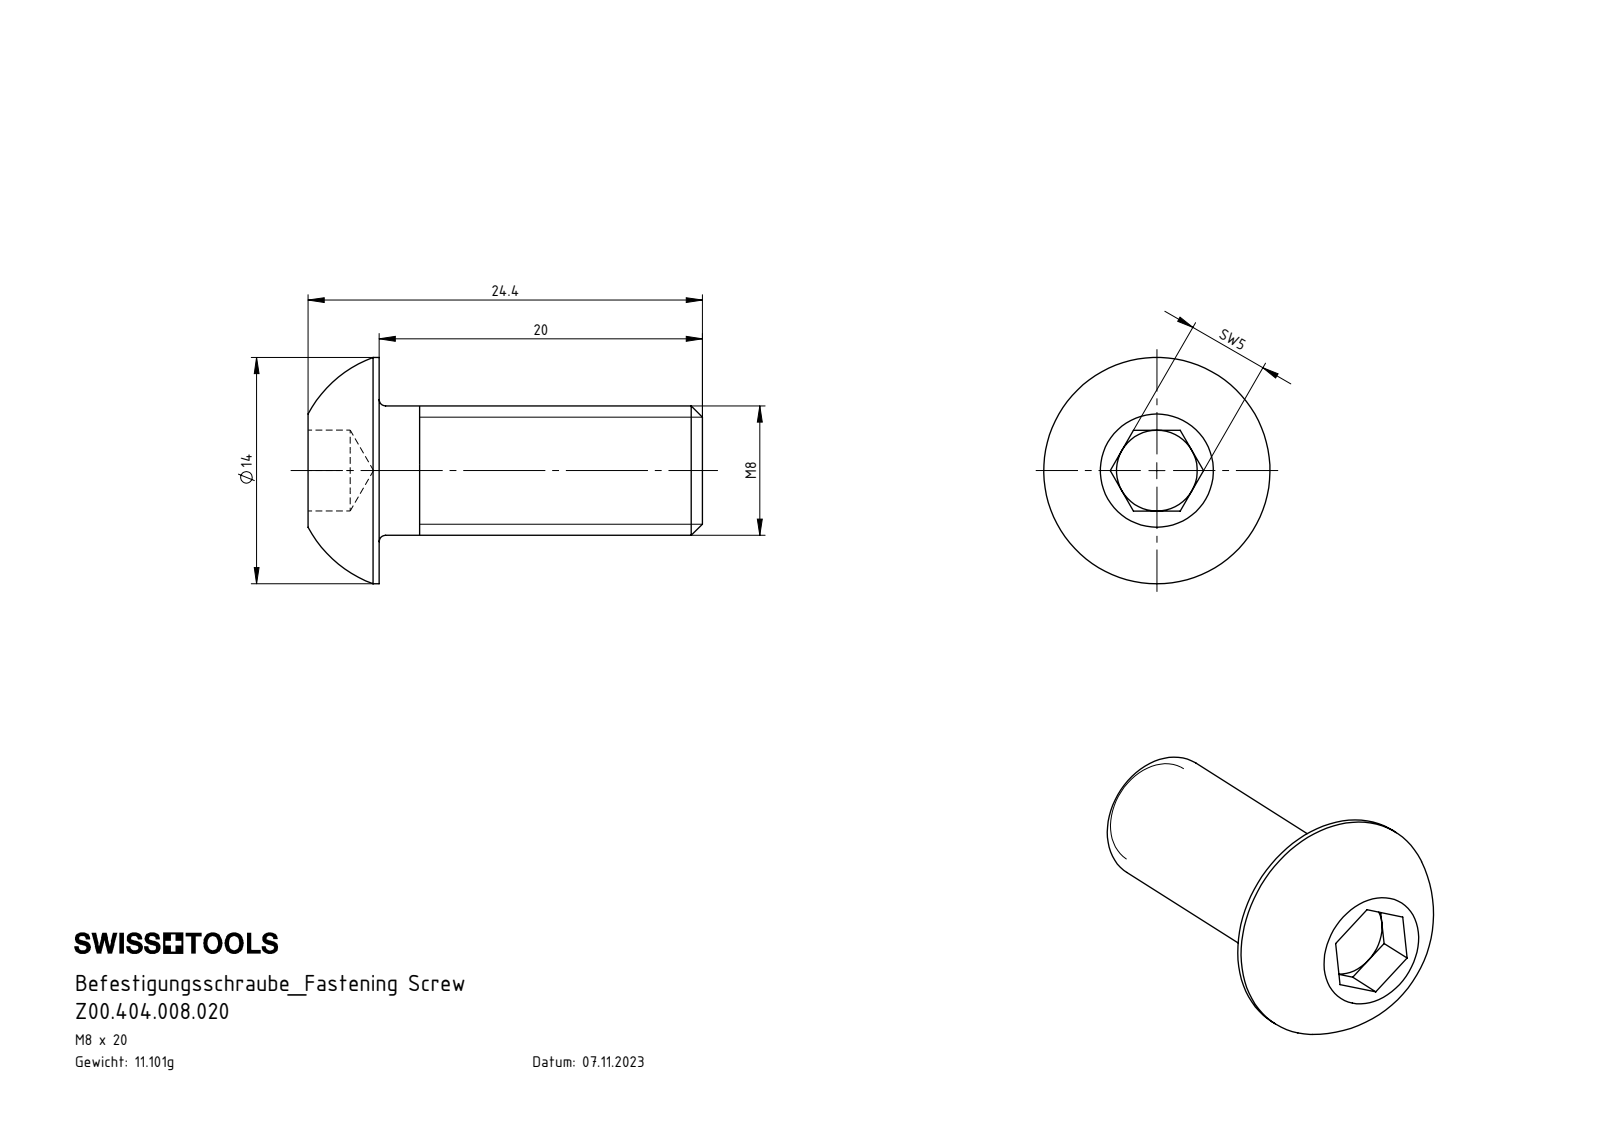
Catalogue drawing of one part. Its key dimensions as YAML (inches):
part_name: "Z00.404.008.020"
step_written_by: "SolidWorks 2022 (AUTOMOTIVE_DESIGN)"
units: inches
bodies: {solids: 1, faces: 27, planar: 15, cylindrical: 4, other: 8}
overall_size: [0.961, 0.551, 0.551]
volume: 0.086
surface_area: 1.45
round_bosses_or_shafts:
  - {diameter: 0.551, count: 1}
  - {diameter: 0.315, count: 1}
face_to_face_distances: [0.787, 0.197, 0.173, 0.961, 0.102, 0.071, 0.858]
